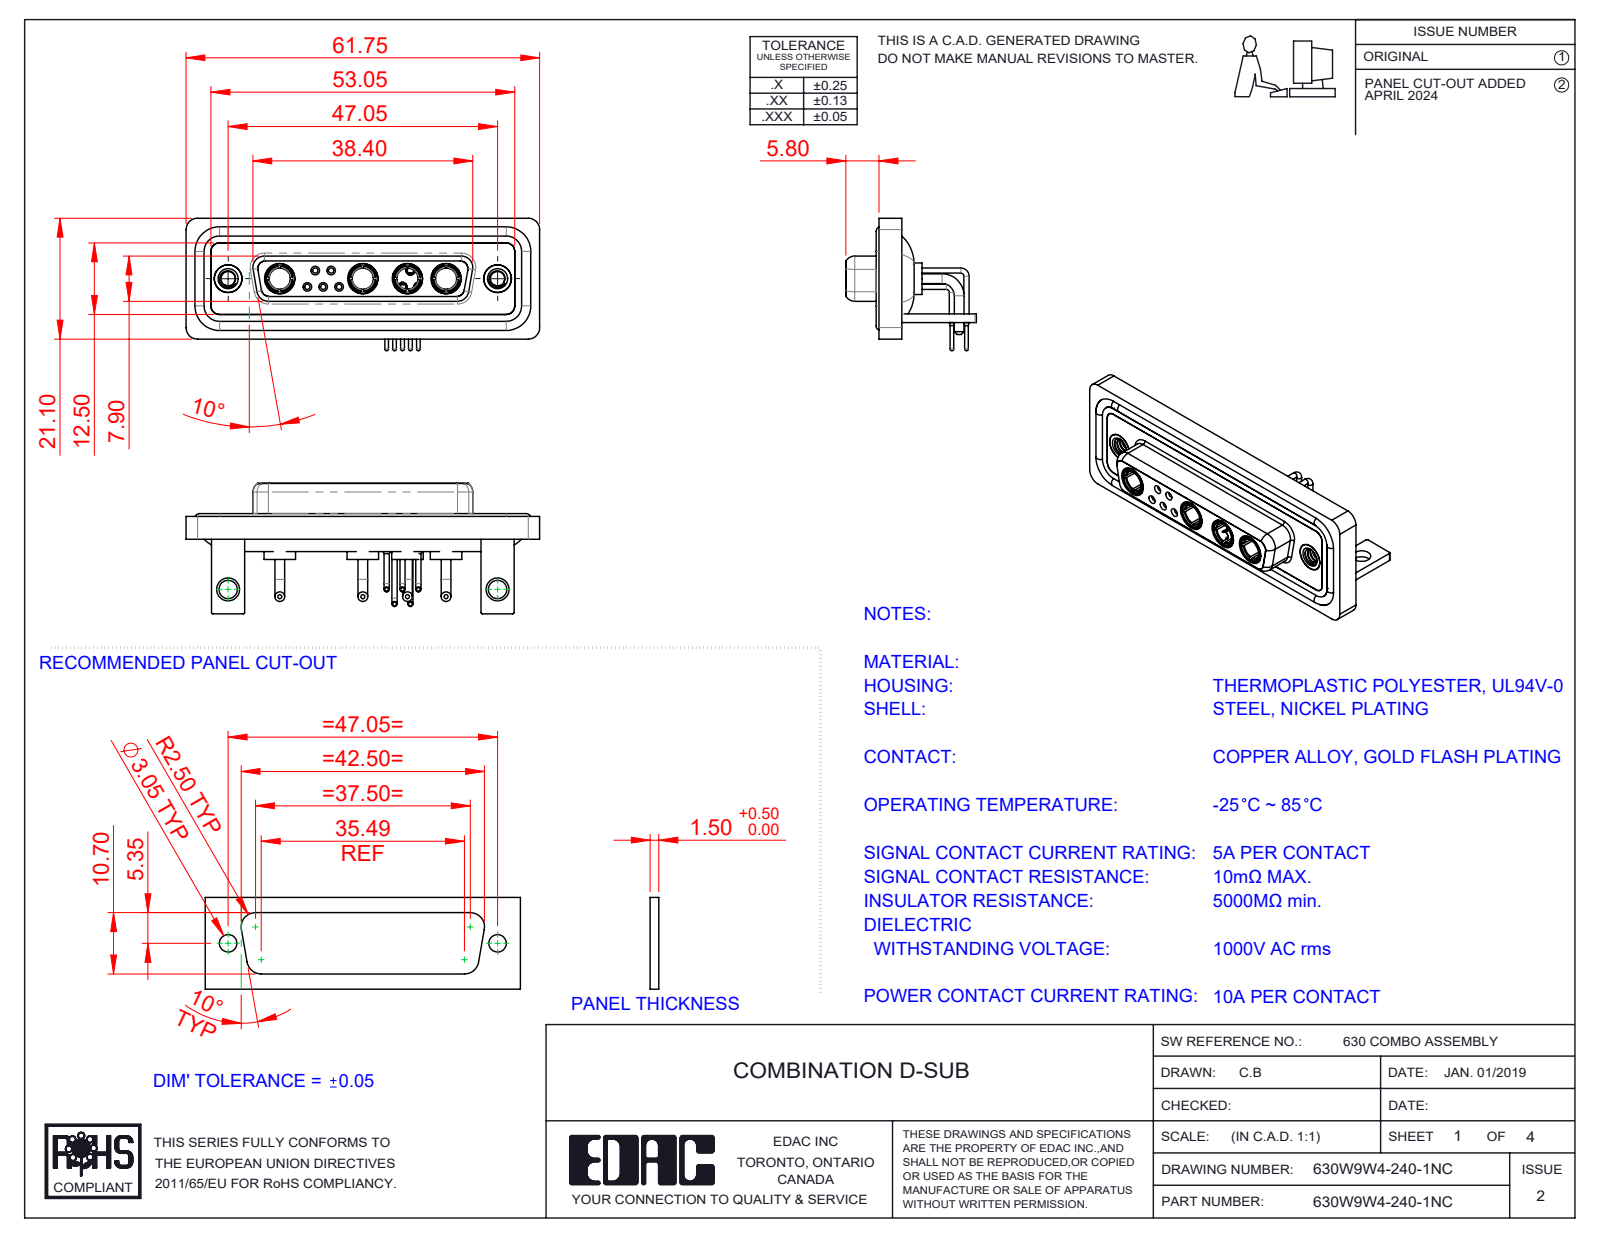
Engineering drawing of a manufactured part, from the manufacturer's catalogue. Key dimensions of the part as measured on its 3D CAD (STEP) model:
Part name (STEP PRODUCT): 630Combo Contact Row 2_50 Contacts; 630Combo Threaded Rivet_A; 630Combo Shell Rear_25 Contacts; 630Combo Shell Front_25 Contacts (+6 more)
STEP written by: SolidWorks 2023 (CONFIG_CONTROL_DESIGN)
Units: millimetres
Bodies: 22 solids, 1005 faces (316 planar, 425 cylindrical, 264 other)
Overall size (bounding box): 61.75 × 23.12 × 22.8
Volume: 8 580 mm³ · Surface area: 14 583 mm²
Round holes (diameter × count): ⌀4.85 ×6, ⌀0.9 ×5, ⌀1.1 ×5, ⌀1.5 ×5, ⌀2 ×5, ⌀3.7 ×4, ⌀5.3 ×4, ⌀1.6 ×3, ⌀1.7 ×2, ⌀2.5 ×2, ⌀3.2 ×2, ⌀4 ×2
Round bosses / shafts (diameter × count): ⌀0.9 ×10, ⌀1.6 ×9, ⌀1.7 ×8, ⌀2 ×5, ⌀1.5 ×5, ⌀0.65 ×5, ⌀5.5 ×4, ⌀5.2 ×4
Partial cylindrical surfaces — rounded edges, fillets, slot ends (radius × count): R2 ×19, R1.5 ×18, R0.25 ×16, R1.35 ×8, R1.6 ×8, R0.5 ×5, R0.6 ×4, R0.65 ×4
Main face-to-face distances: 0.4, 1.8, 2.9, 3.7, 1.5, 4.1, 1.1, 1.4, 1.6, 2.5
Hole centre spacings: 3.16, 2.77, 5.04, 13.85, 11.08, 12.79, 15.5, 5.54
